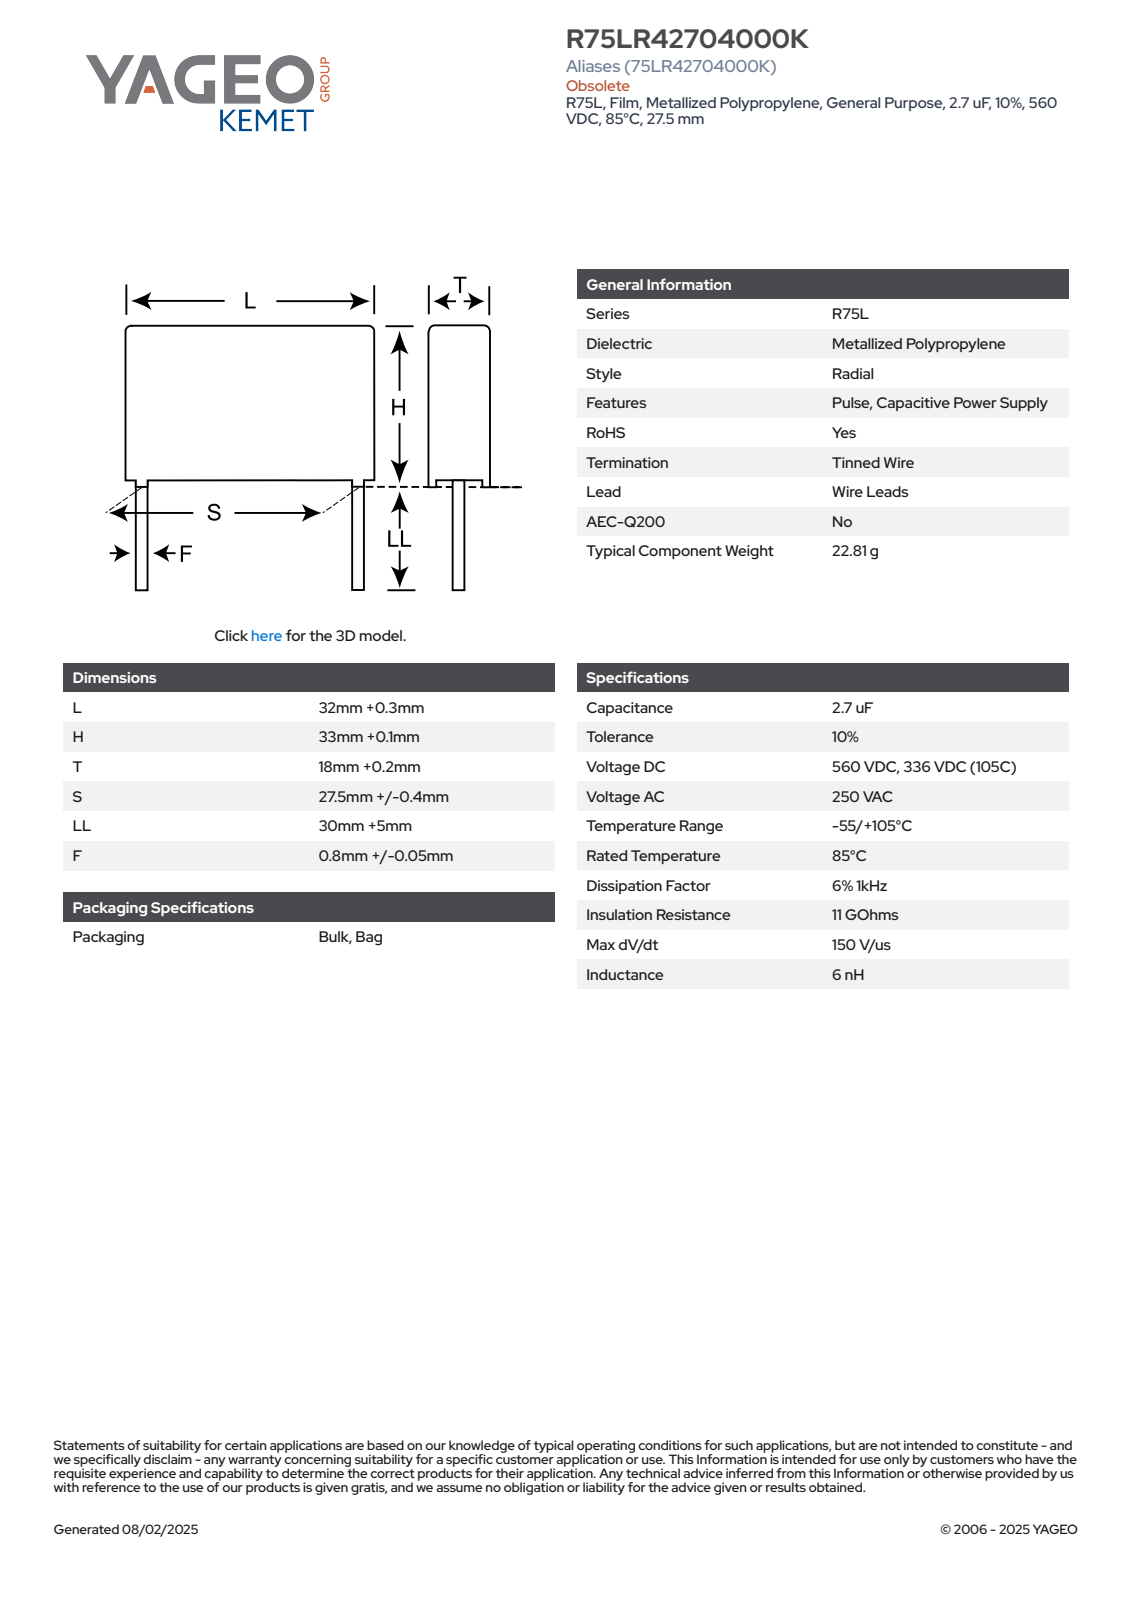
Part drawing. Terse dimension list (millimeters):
name: CFR_RB3_32X33X18_L32.3H33.1T18.2S27.5LL35F0.85
written by: SolidWorks 2014 (AUTOMOTIVE_DESIGN)
unit: mm
bodies: 4 solids, 85 faces (77 planar, 8 cylindrical, 0 other)
size: 68.1 × 32.3 × 18.2
volume: 18 928 mm³; area: 4 754 mm²
bosses: 2× ⌀0.85
rounds: 4× R0.5
face distances: 18.2, 32.3, 31.96, 0.39, 32.35, 0.75, 1.14, 33.1, 1.08, 31.22
